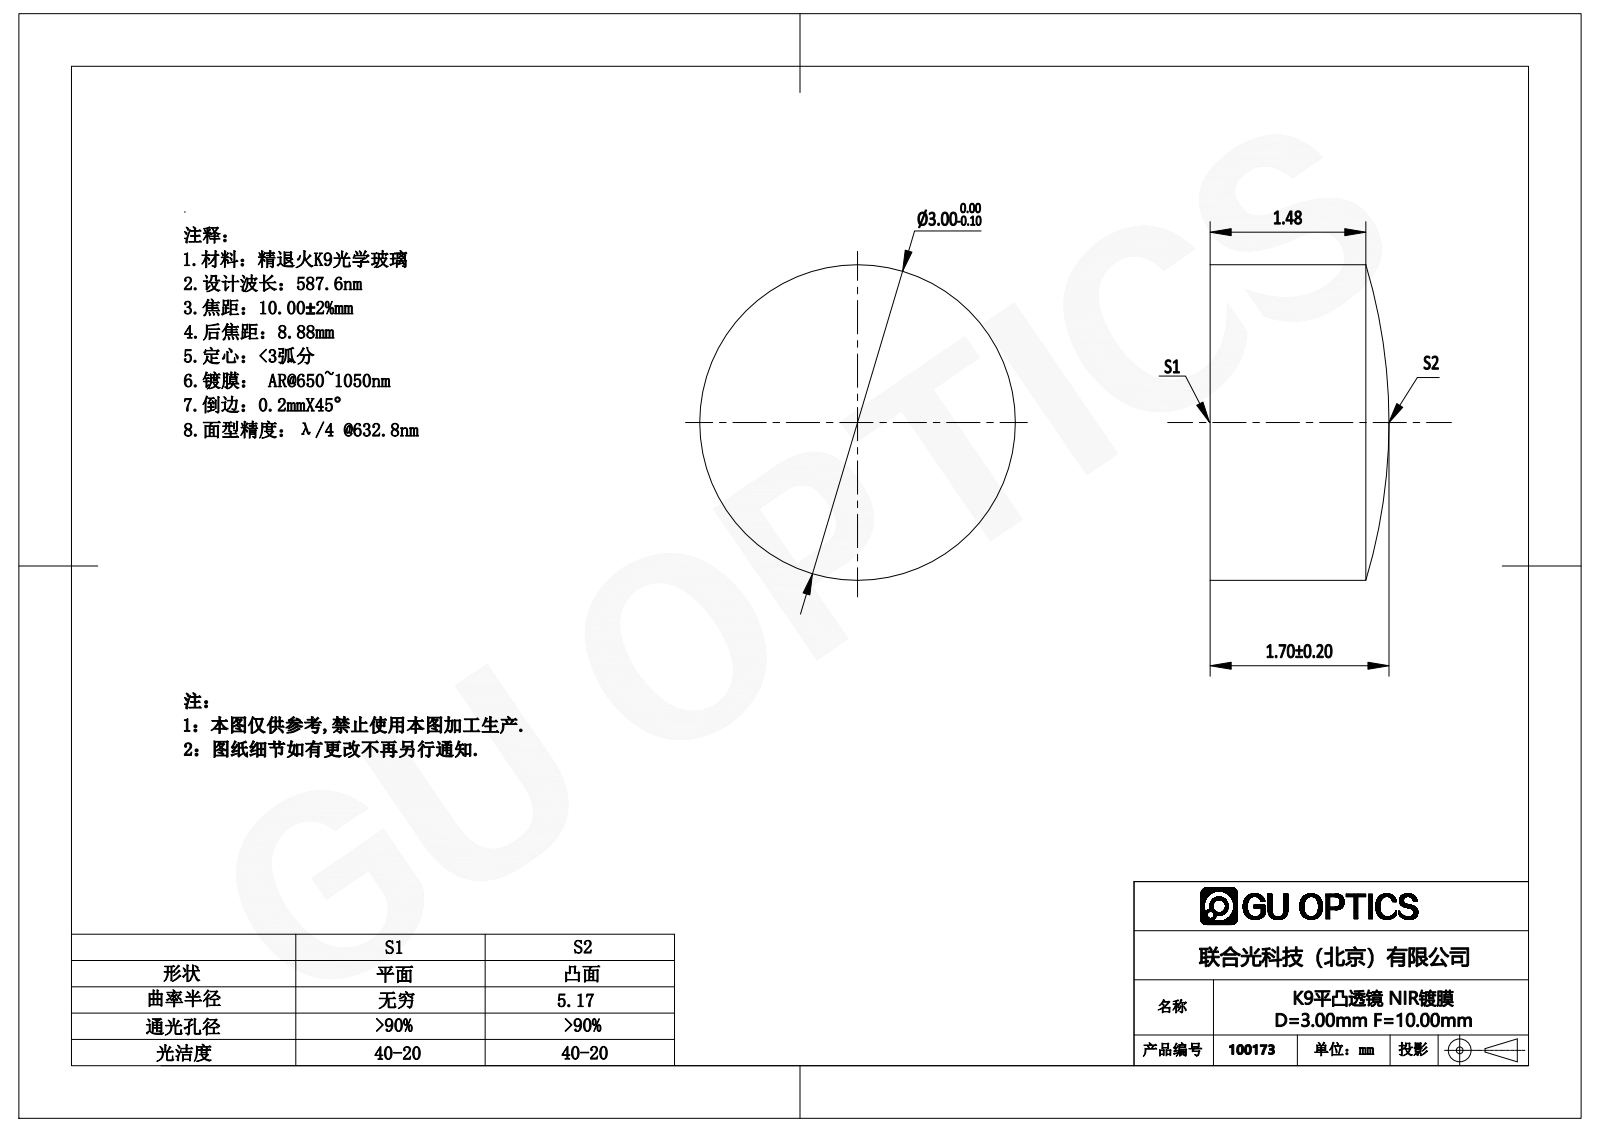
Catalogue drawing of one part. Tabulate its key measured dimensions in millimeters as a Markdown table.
| quantity | value |
| --- | --- |
| part name | 100173 |
| STEP written by | SolidWorks 2016 (AUTOMOTIVE_DESIGN) |
| units | millimeters |
| bodies | 1 solid, 5 faces (1 planar, 2 cylindrical, 2 other) |
| overall size | 3 × 3 × 1.7 |
| volume | 11 mm³ |
| surface area | 28 mm² |
| round bosses / shafts (diameter × count) | 3 × 1 |
